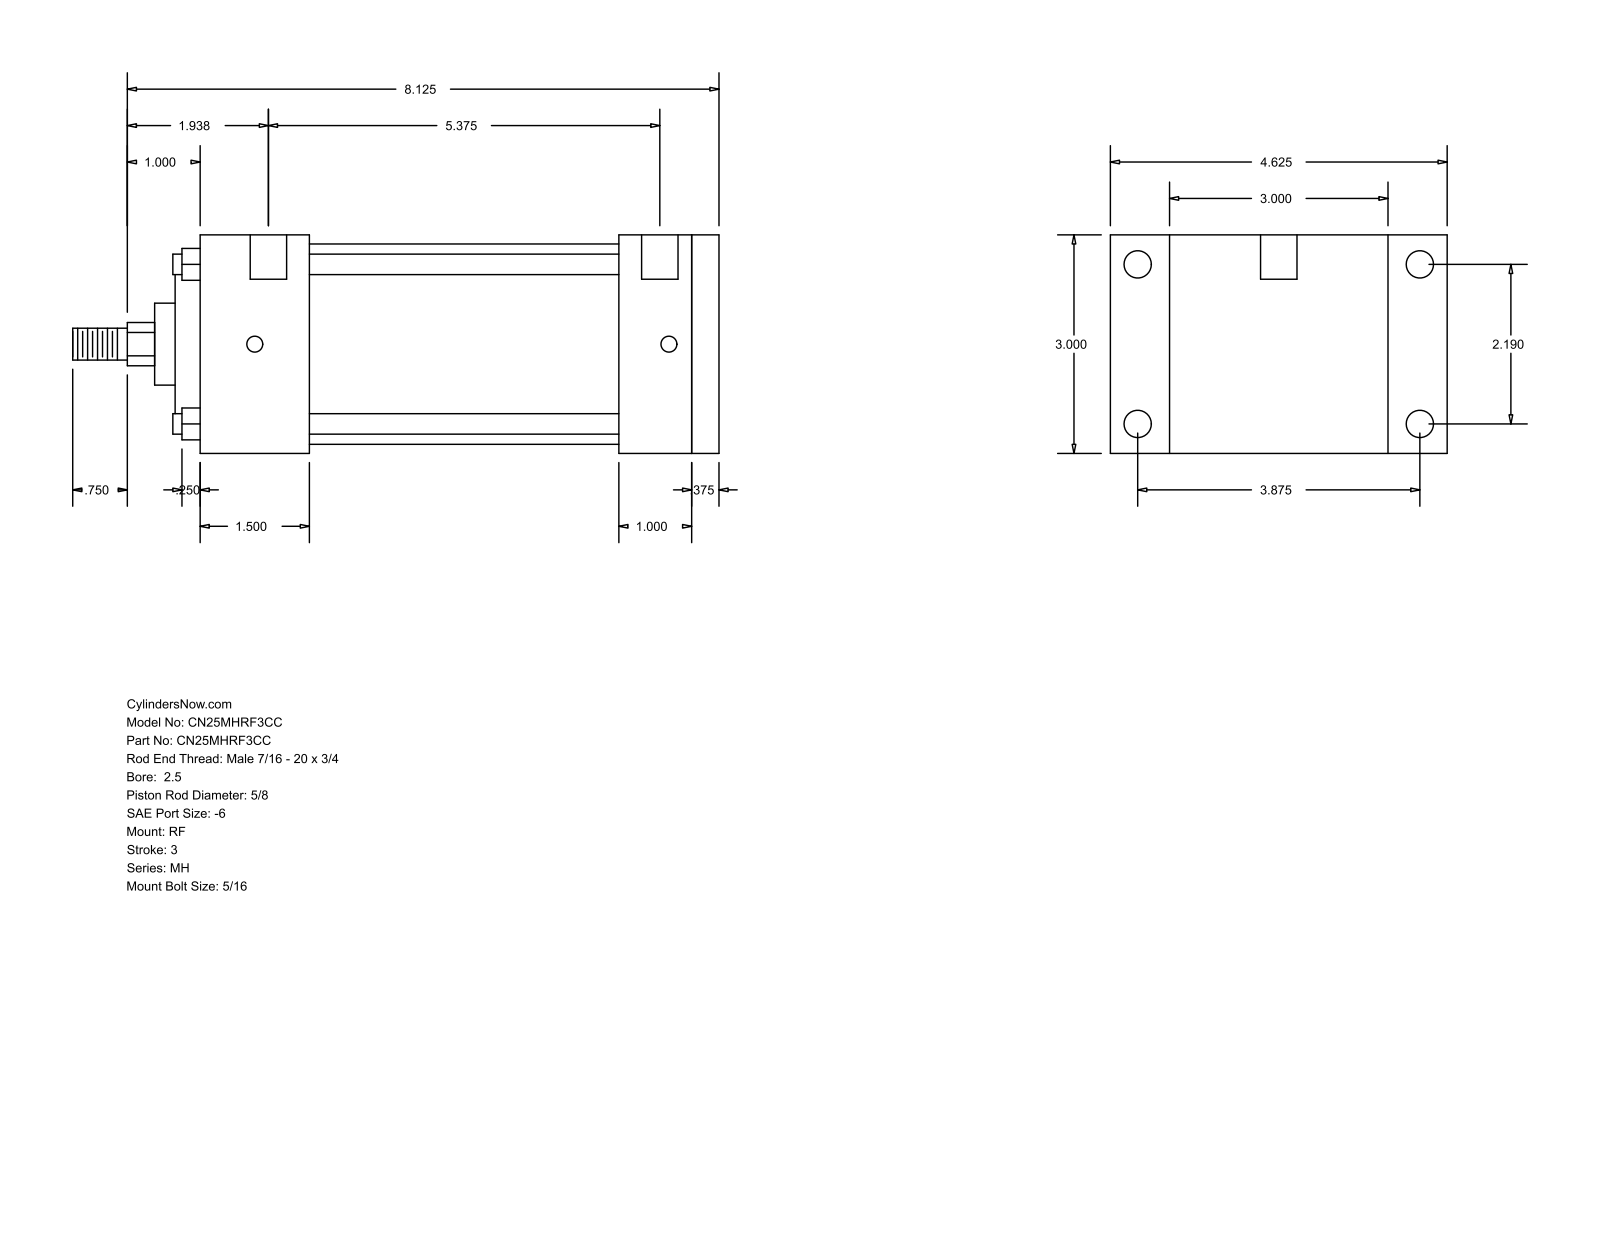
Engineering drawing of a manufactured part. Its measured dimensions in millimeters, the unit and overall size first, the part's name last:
Units: millimetres
Overall size (bounding box): 225.43 × 117.47 × 76.2
Round holes (diameter × count): ⌀5.56 ×4, ⌀9.53 ×4, ⌀12.7 ×2
Round bosses / shafts (diameter × count): ⌀7.14 ×4, ⌀69.85 ×1, ⌀55.55 ×1, ⌀28.57 ×1, ⌀15.88 ×1, ⌀11.11 ×1
Partial cylindrical surfaces — rounded edges, fillets, slot ends (radius × count): R7.54 ×1
Main face-to-face distances: 76.2, 9.53, 180.98, 171.45, 25.4, 34.93, 38.1, 146.05, 107.95, 133.35
Hole centre spacings: 55.62, 98.42, 113.05, 144.46, 3.17, 4.76, 136.53, 139.7
Bodies: 0 solids, 94 faces (65 planar, 29 cylindrical, 0 other)
Part name (STEP PRODUCT): MH_RF__0250_0.625
STEP written by: GSSL Pune (CONFIG_CONTROL_DESIGN)
